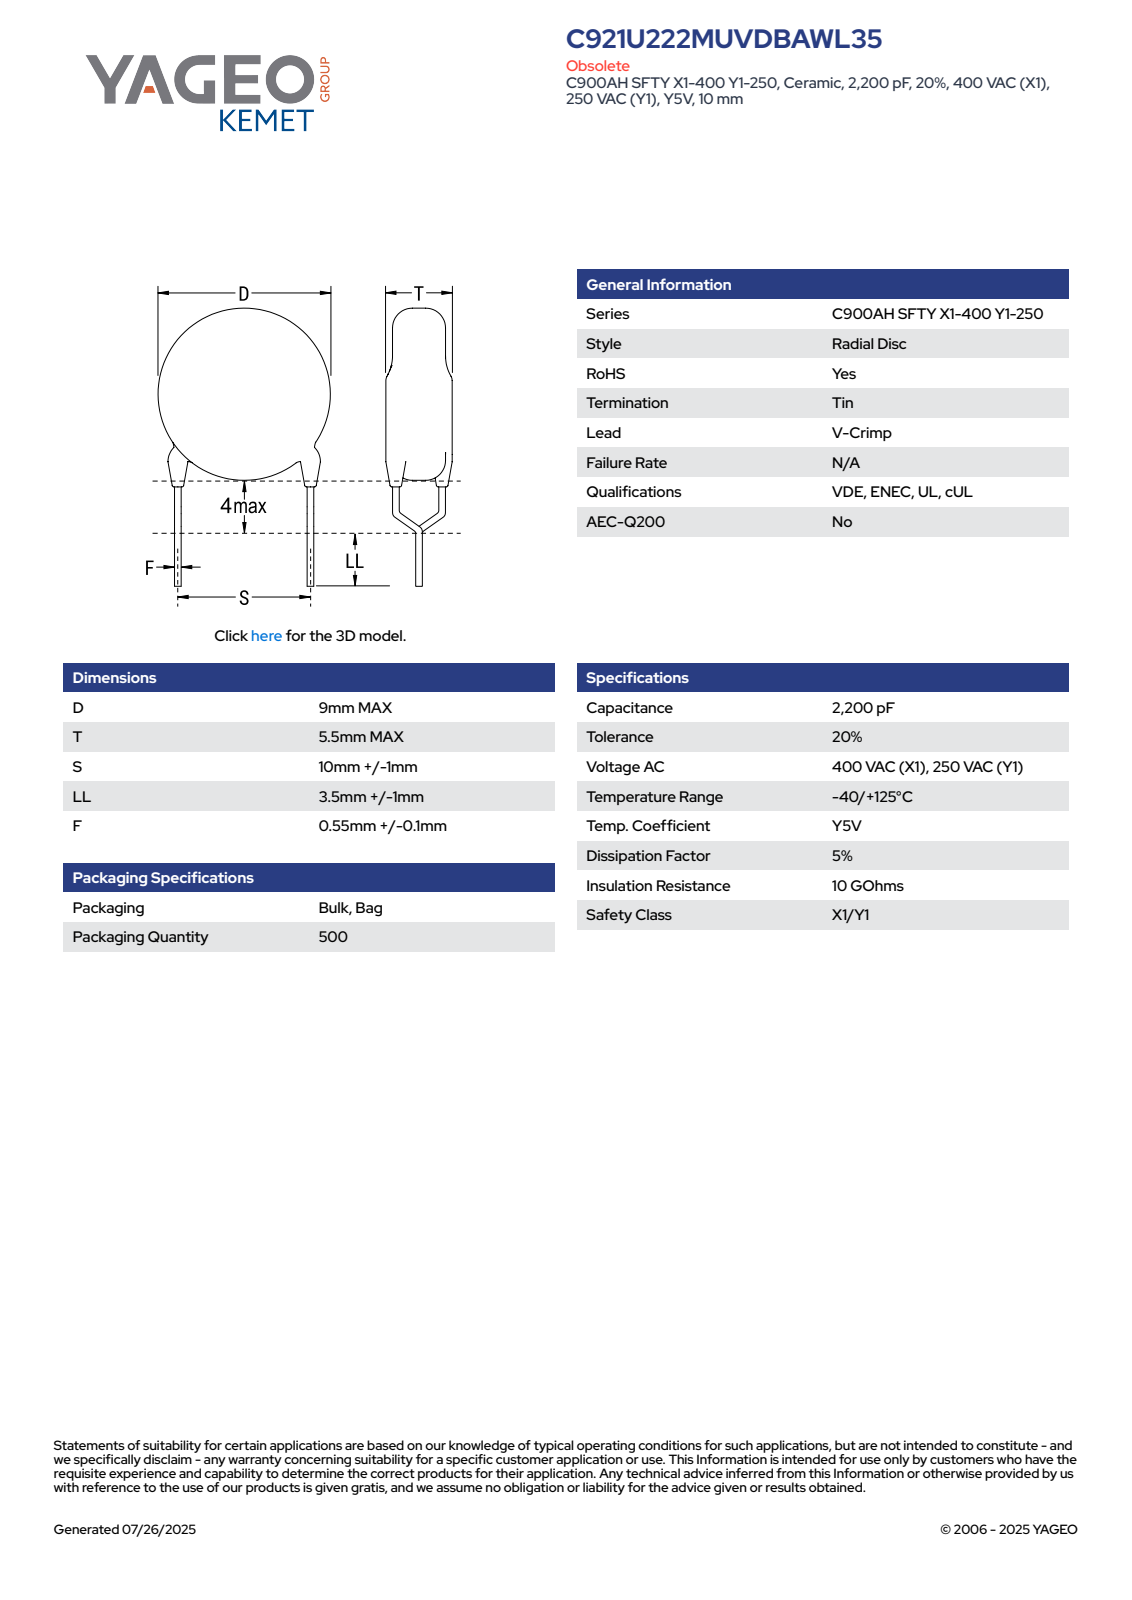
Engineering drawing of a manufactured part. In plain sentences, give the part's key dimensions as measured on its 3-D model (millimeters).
The part is named "CCD_VCC900_D9T5.5S10LL4.5F0.65". Its 3-D file was written by "SolidWorks 2014 (AUTOMOTIVE_DESIGN)". It is 5 solids with 93 faces: 65 planar, 16 cylindrical and 12 other. Overall it measures 17.3 by 10.65 by 5.5 millimeters. Its volume is 349 cubic millimeters and its surface area 316 square millimeters. Round bosses or shafts: 6 of diameter 0.65, 1 of diameter 9. The main face-to-face distances are 5.5, 7.4, 1.17, 13.38, 5.98, 12.21, 4.81, 0.32, 4.77, 3.47.
